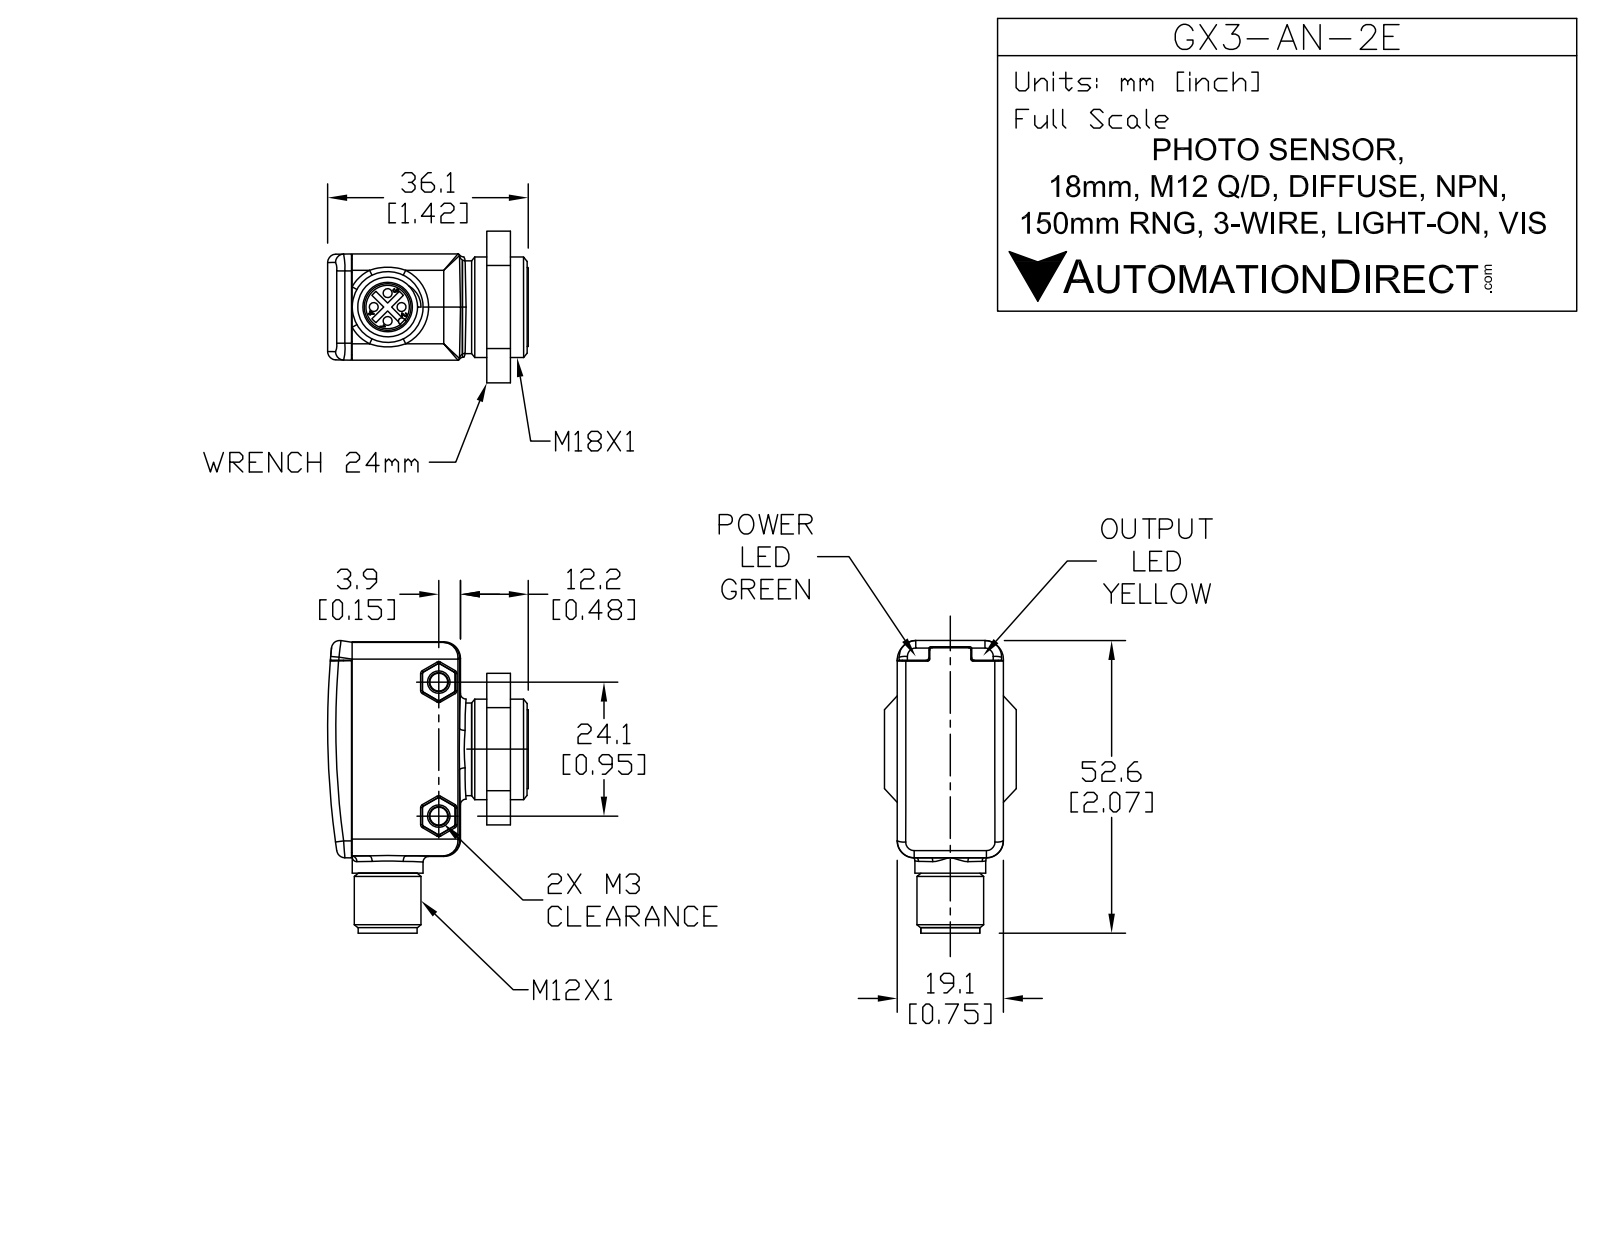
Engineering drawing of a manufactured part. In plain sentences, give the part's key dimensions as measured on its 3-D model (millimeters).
The part is named "GX3-AN-2E". Its 3-D file was written by "SolidWorks 2013 (AUTOMOTIVE_DESIGN)". It is 1 solid with 107 faces: 60 planar, 33 cylindrical and 14 other. Overall it measures 52.66 by 36.1 by 23.85 millimeters. Its volume is 21 253 cubic millimeters and its surface area 6 452 square millimeters. Round holes: 2 of diameter 3.2, 1 of diameter 8.36. Round bosses or shafts: 1 of diameter 18, 1 of diameter 17.5, 1 of diameter 14.2, 1 of diameter 12.68, 1 of diameter 11.55, 1 of diameter 10.6. Partial cylindrical surfaces (rounded edges, fillets, slot ends): 8 of radius 1.5, 4 of radius 1, 1 of radius 139.57. The main face-to-face distances are 19.1, 7.2, 2.12, 9.32, 19.2, 5, 2.88, 12.2, 38.8, 5.95. The hole center spacings are 24.1.
